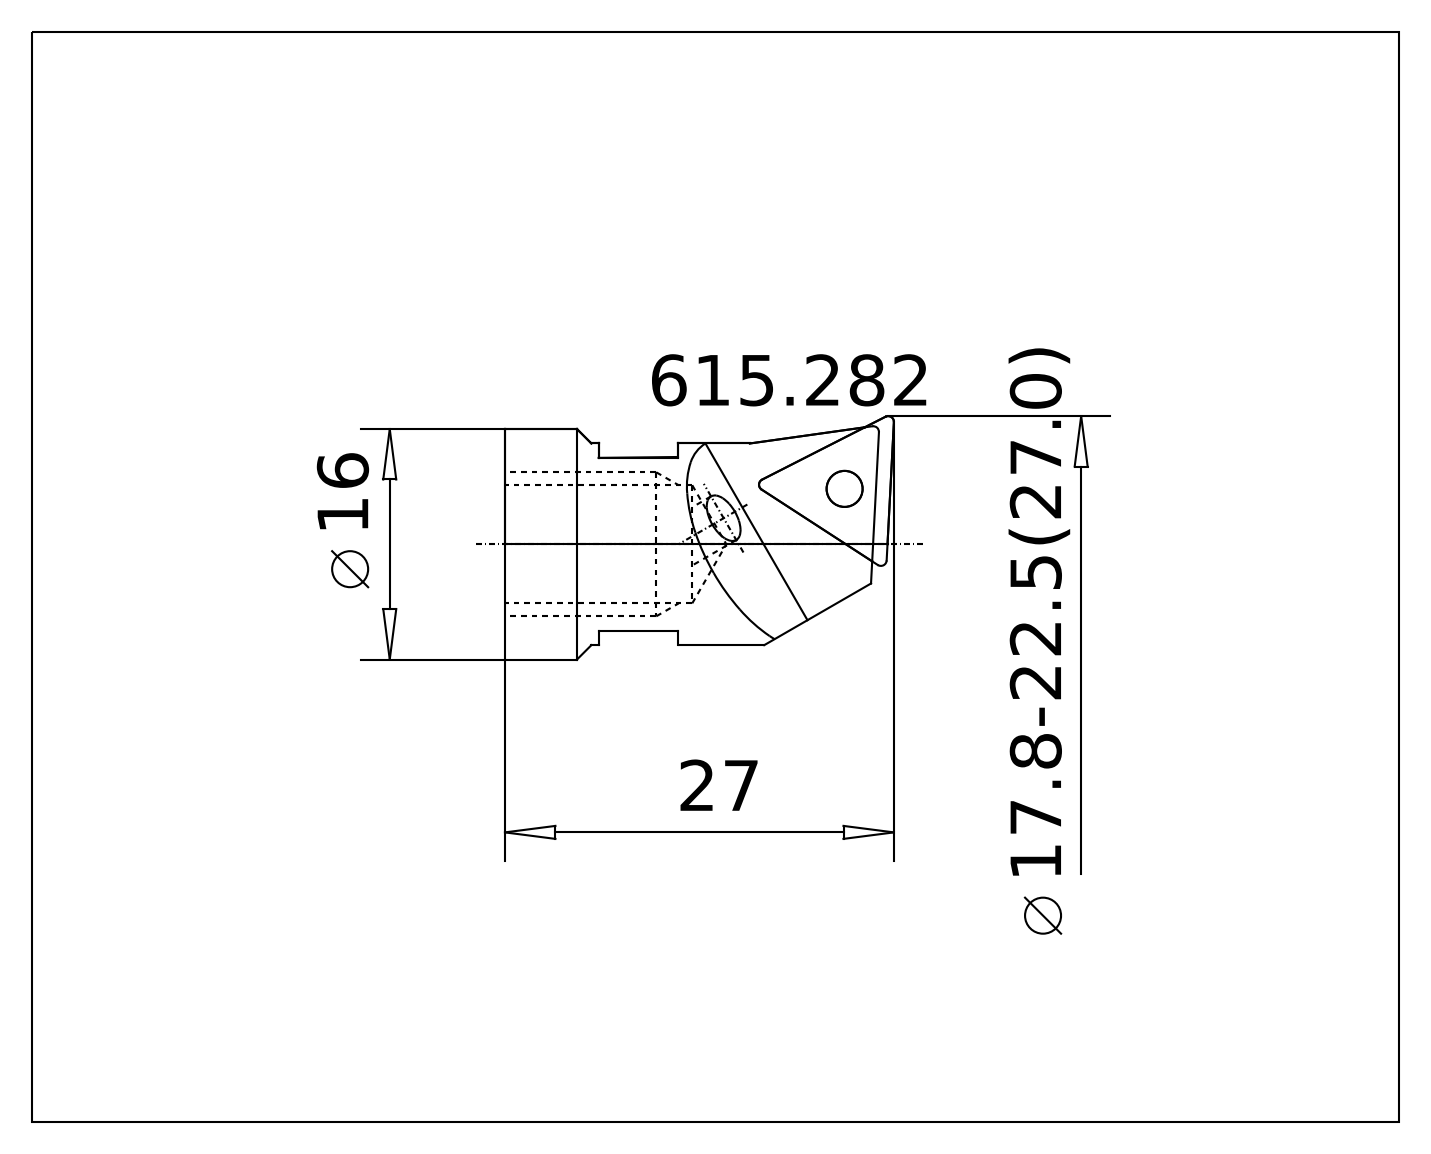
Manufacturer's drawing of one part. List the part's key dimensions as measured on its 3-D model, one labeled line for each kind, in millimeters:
Part name (STEP PRODUCT): 615.282 Kaiser E18 TC11|655.383 Kaiser TCGT 110204 K10C;Kombinieren1; 615.282 Kaiser E18 TC11|694.122 Kaiser ETL M2.5x6.5 T7 IP 10S;Kreismuster1; 615.282 Kaiser E18 TC11|615.282 Kaiser E18 TC11;Verrundung4
STEP written by: ACIS (automotive_design)
Units: millimetres
Bodies: 3 solids, 132 faces (30 planar, 53 cylindrical, 49 other)
Overall size (bounding box): 27 × 16.85 × 16
Volume: 2 497 mm³ · Surface area: 2 124 mm²
Round holes (diameter × count): ⌀2 ×1, ⌀2.5 ×1, ⌀2.8 ×1, ⌀8.5 ×1, ⌀10 ×1
Round bosses / shafts (diameter × count): ⌀16 ×1, ⌀14 ×1, ⌀3.45 ×1, ⌀2.5 ×1
Partial cylindrical surfaces — rounded edges, fillets, slot ends (radius × count): R0.15 ×6, R0.4 ×6, R0.2 ×4, R3 ×2, R1.6 ×1, R6 ×1, R6.8 ×1
Main face-to-face distances: 2.38, 12, 11.01, 11, 1, 10, 5.3, 7.68, 7.4, 2.1
